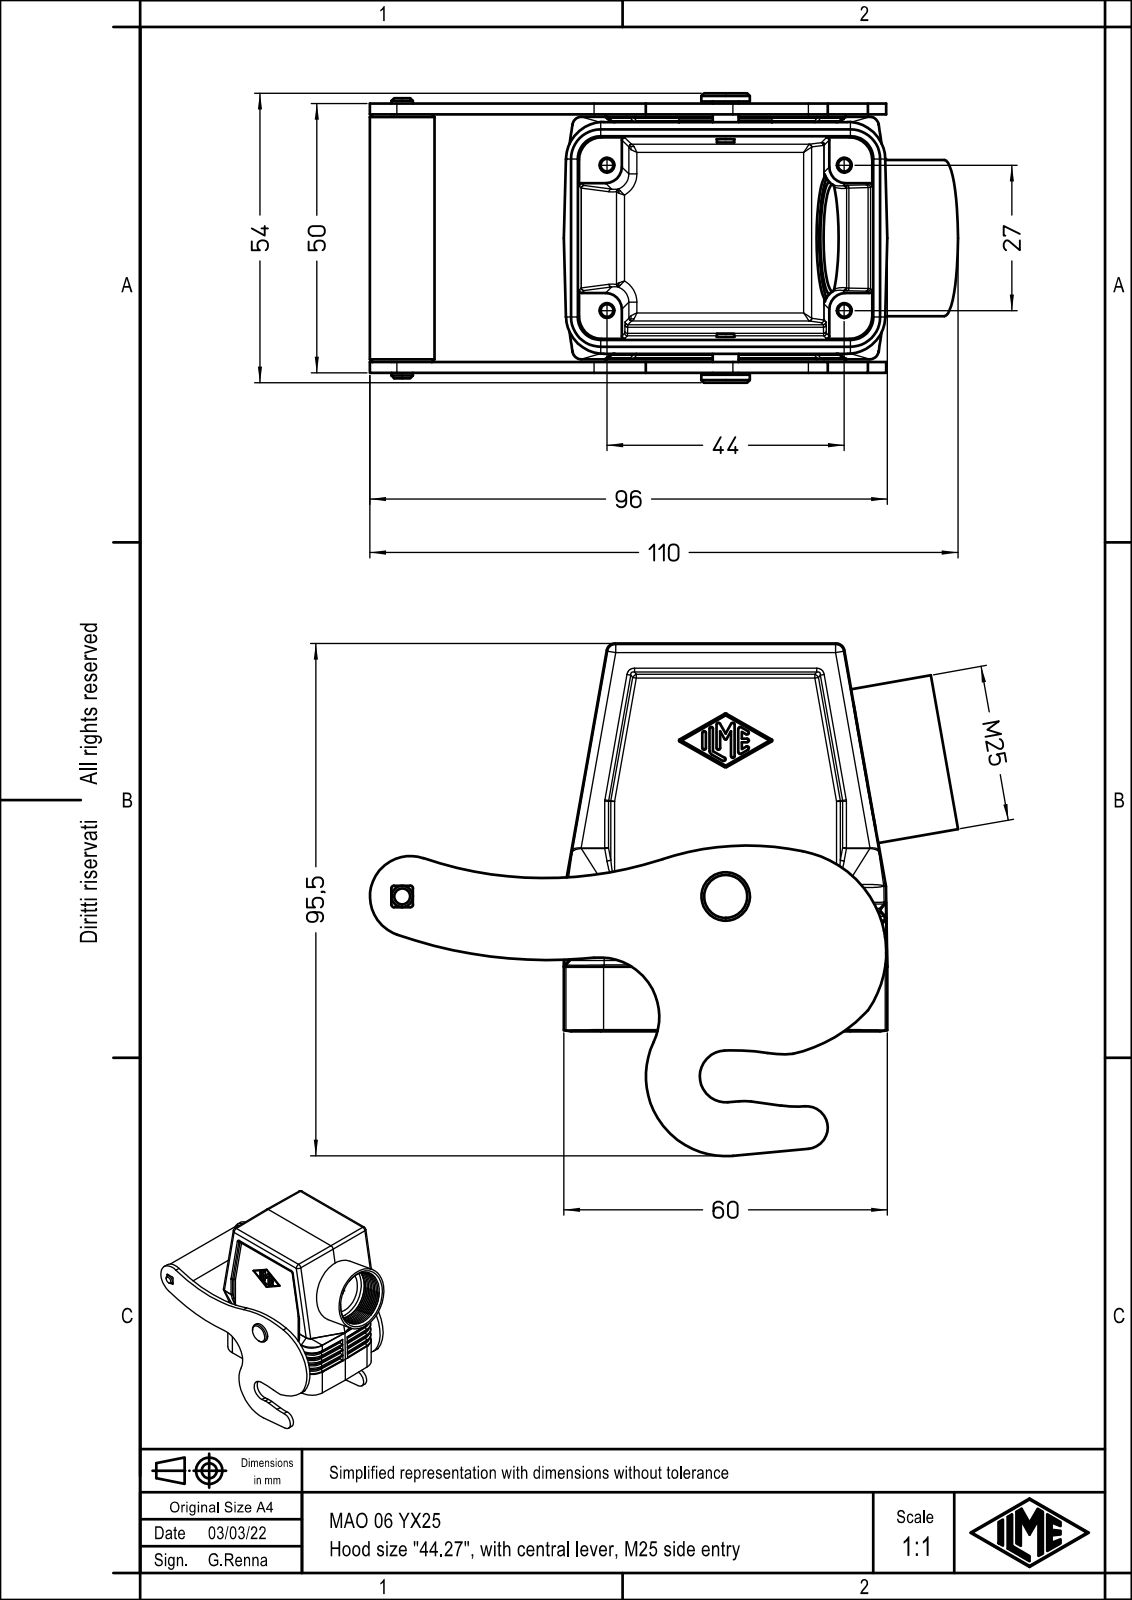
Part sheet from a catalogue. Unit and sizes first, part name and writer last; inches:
Units: inches
Overall size (bounding box): 4.296 × 3.747 × 2.116
Round holes (diameter × count): ⌀0.128 ×1, ⌀0.787 ×1, ⌀0.929 ×1, ⌀0.984 ×1
Round bosses / shafts (diameter × count): ⌀1.142 ×1, ⌀0.906 ×1, ⌀0.472 ×1, ⌀0.354 ×1, ⌀0.189 ×1, ⌀0.156 ×1, ⌀0.126 ×1
Partial cylindrical surfaces — rounded edges, fillets, slot ends (radius × count): R0.02 ×79, R0.039 ×34, R0.059 ×20, R0.013 ×15, R0.276 ×8, R0.118 ×4, R0.165 ×4, R0.007 ×3
Main face-to-face distances: 0.079, 1.89, 1.969, 1.811, 0.139, 0.06, 1.83, 1.751, 0.137, 0.058
Volume: 4.897 in³ · Surface area: 71.42 in²
Bodies: 1 solid, 2119 faces (1590 planar, 252 cylindrical, 277 other)
Part name (STEP PRODUCT): MAO 06 YX25
STEP written by: Creo Elements/Direct Modeling 20.1B 02-Apr-2019 (C) Parametric Technology GmbH (AUTOMOTIVE_DESIGN)
